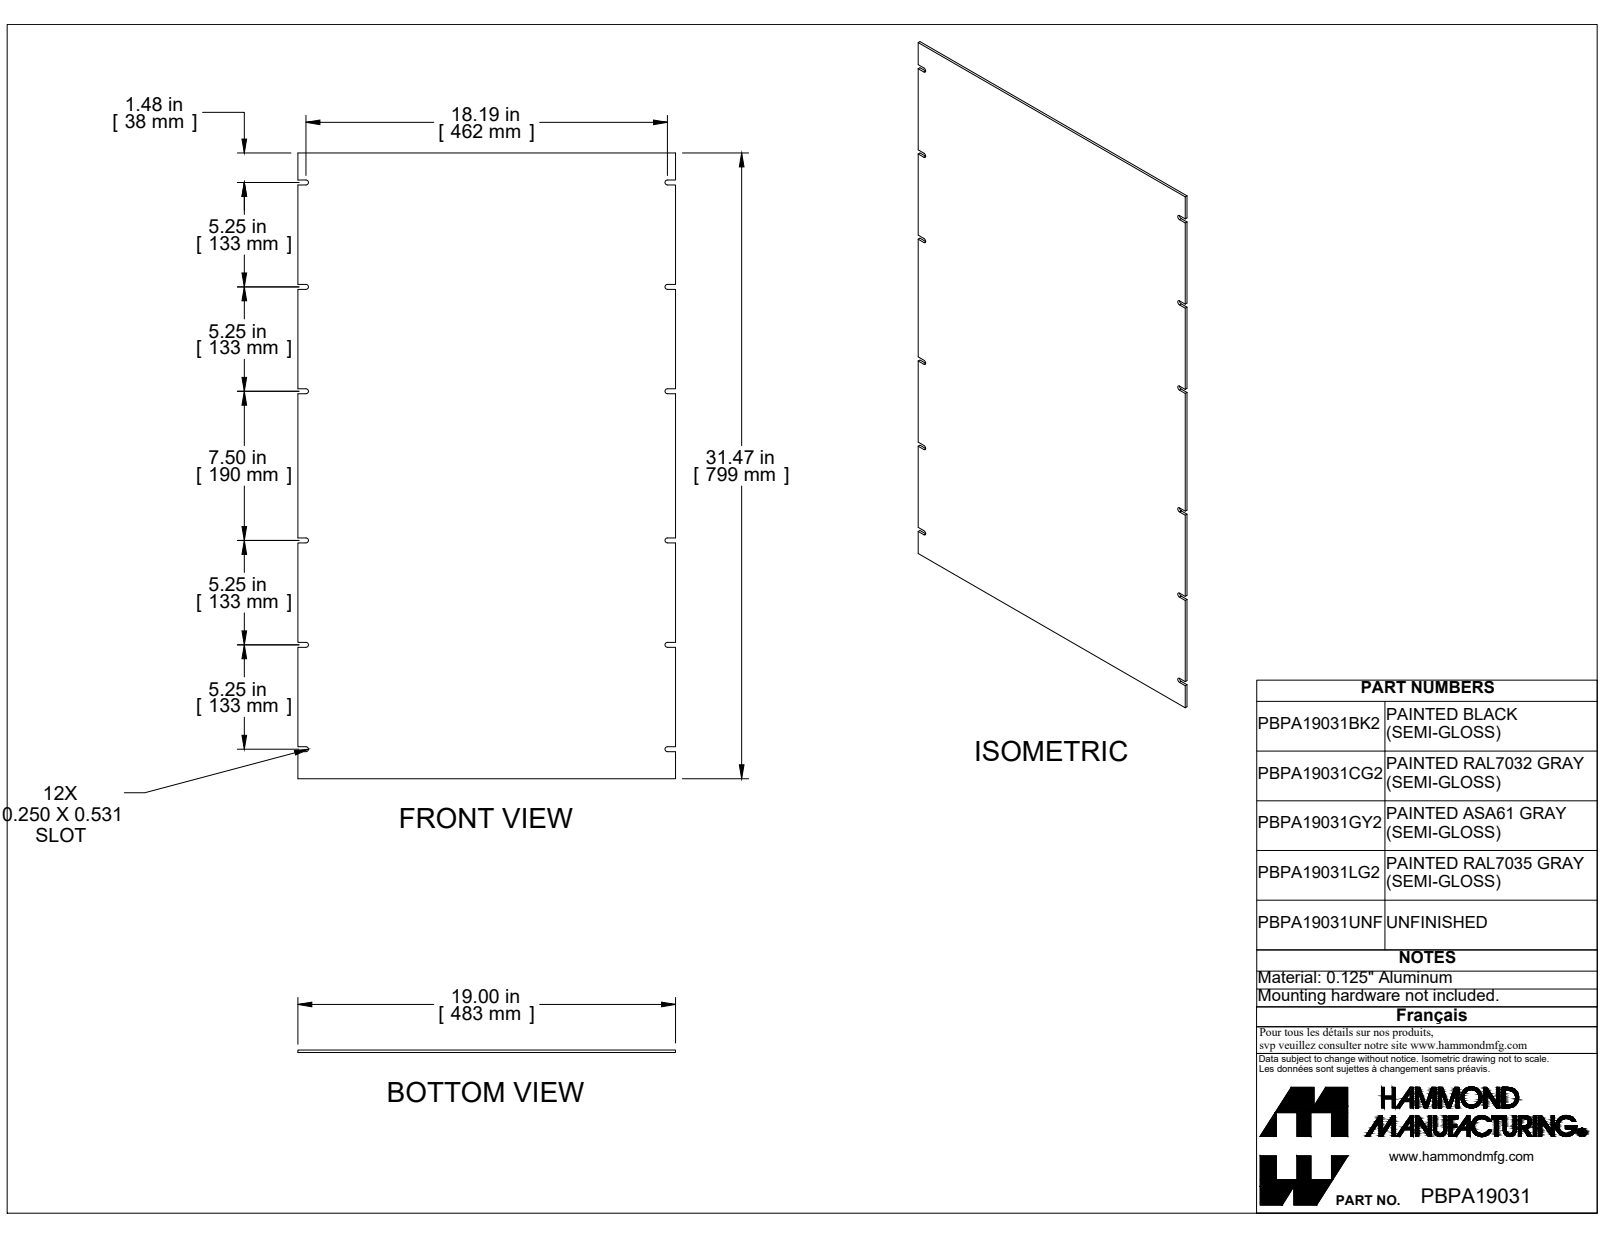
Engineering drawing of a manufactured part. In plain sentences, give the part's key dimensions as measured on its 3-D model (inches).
The part is named "PBPA19031GY2". Its 3-D file was written by "SolidWorks 2019 (CONFIG_CONTROL_DESIGN)". It is 1 solid with 54 faces: 42 planar, 12 cylindrical and 0 other. Overall it measures 31.468 by 19 by 0.125 inches. Its volume is 74.55 cubic inches and its surface area 1 207 square inches. Partial cylindrical surfaces (rounded edges, fillets, slot ends): 12 of radius 0.125. The main face-to-face distances are 0.125, 19, 31.468, 5.25, 23.25, 18, 0.25, 5, 18.25, 1.359.
